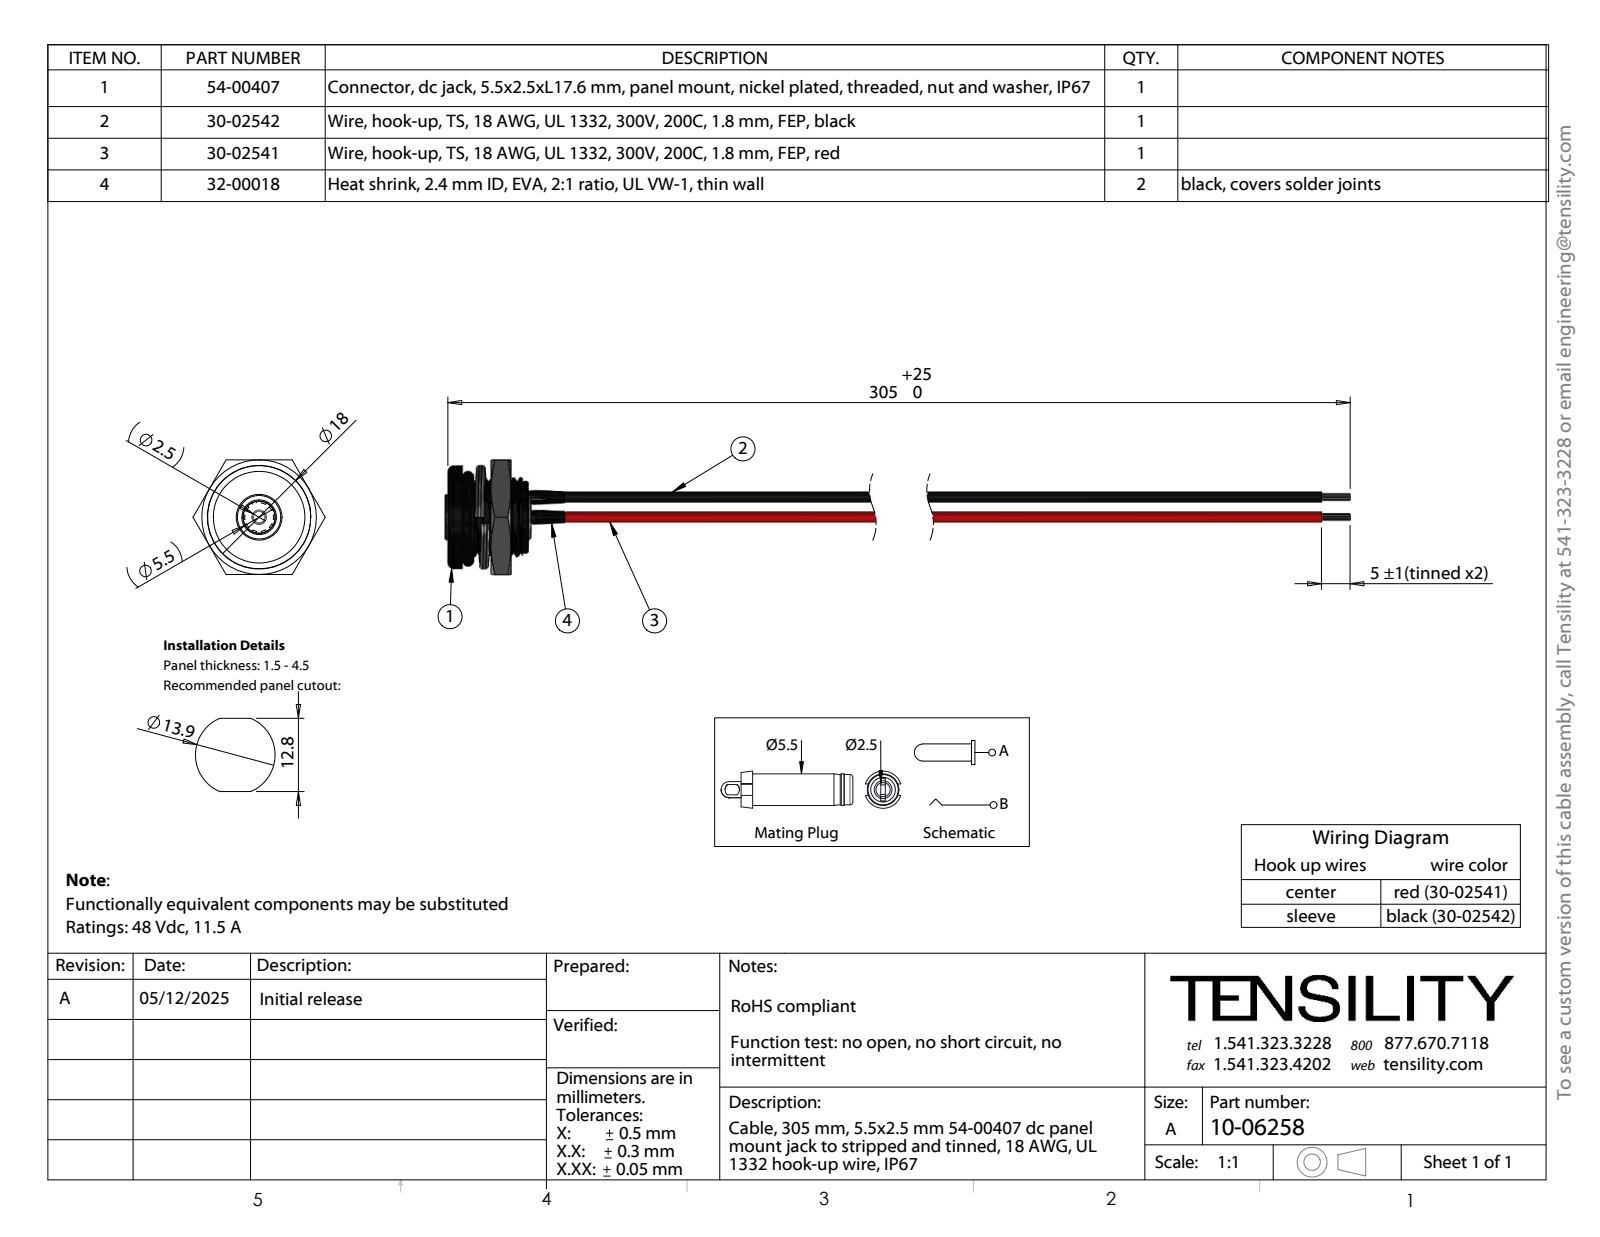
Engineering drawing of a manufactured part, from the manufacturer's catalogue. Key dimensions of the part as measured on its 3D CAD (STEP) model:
Part name (STEP PRODUCT): 55-00308; 56-00029; 24-00419; 50-01012 center pin_Center pin (+8 more)
STEP written by: SolidWorks 2021 (CONFIG_CONTROL_DESIGN)
Units: millimetres
Bodies: 50 solids, 537 faces (185 planar, 237 cylindrical, 115 other)
Overall size (bounding box): 169.62 × 23.09 × 20
Volume: 3 642 mm³ · Surface area: 14 632 mm²
Round holes (diameter × count): ⌀0.24 ×38, ⌀1.5 ×2, ⌀1.6 ×1, ⌀2.15 ×1, ⌀2.5 ×1, ⌀5.6 ×1, ⌀5.65 ×1, ⌀6.4 ×1, ⌀6.6 ×1, ⌀7.6 ×1, ⌀8 ×1, ⌀10 ×1
Round bosses / shafts (diameter × count): ⌀1.8 ×2, ⌀18 ×1, ⌀12.6 ×1, ⌀12.59 ×1, ⌀7.3 ×1, ⌀6.2 ×1, ⌀2.1 ×1
Partial cylindrical surfaces — rounded edges, fillets, slot ends (radius × count): R0.5 ×2, R3.35 ×1, R6.9 ×1
Main face-to-face distances: 3.5, 7.51, 11.01, 2.5, 5.01, 8.51, 20, 8.5, 2, 1
Hole centre spacings: 0.65, 0.43, 0.49, 0.42, 0.85, 0.88, 0.89, 0.73
